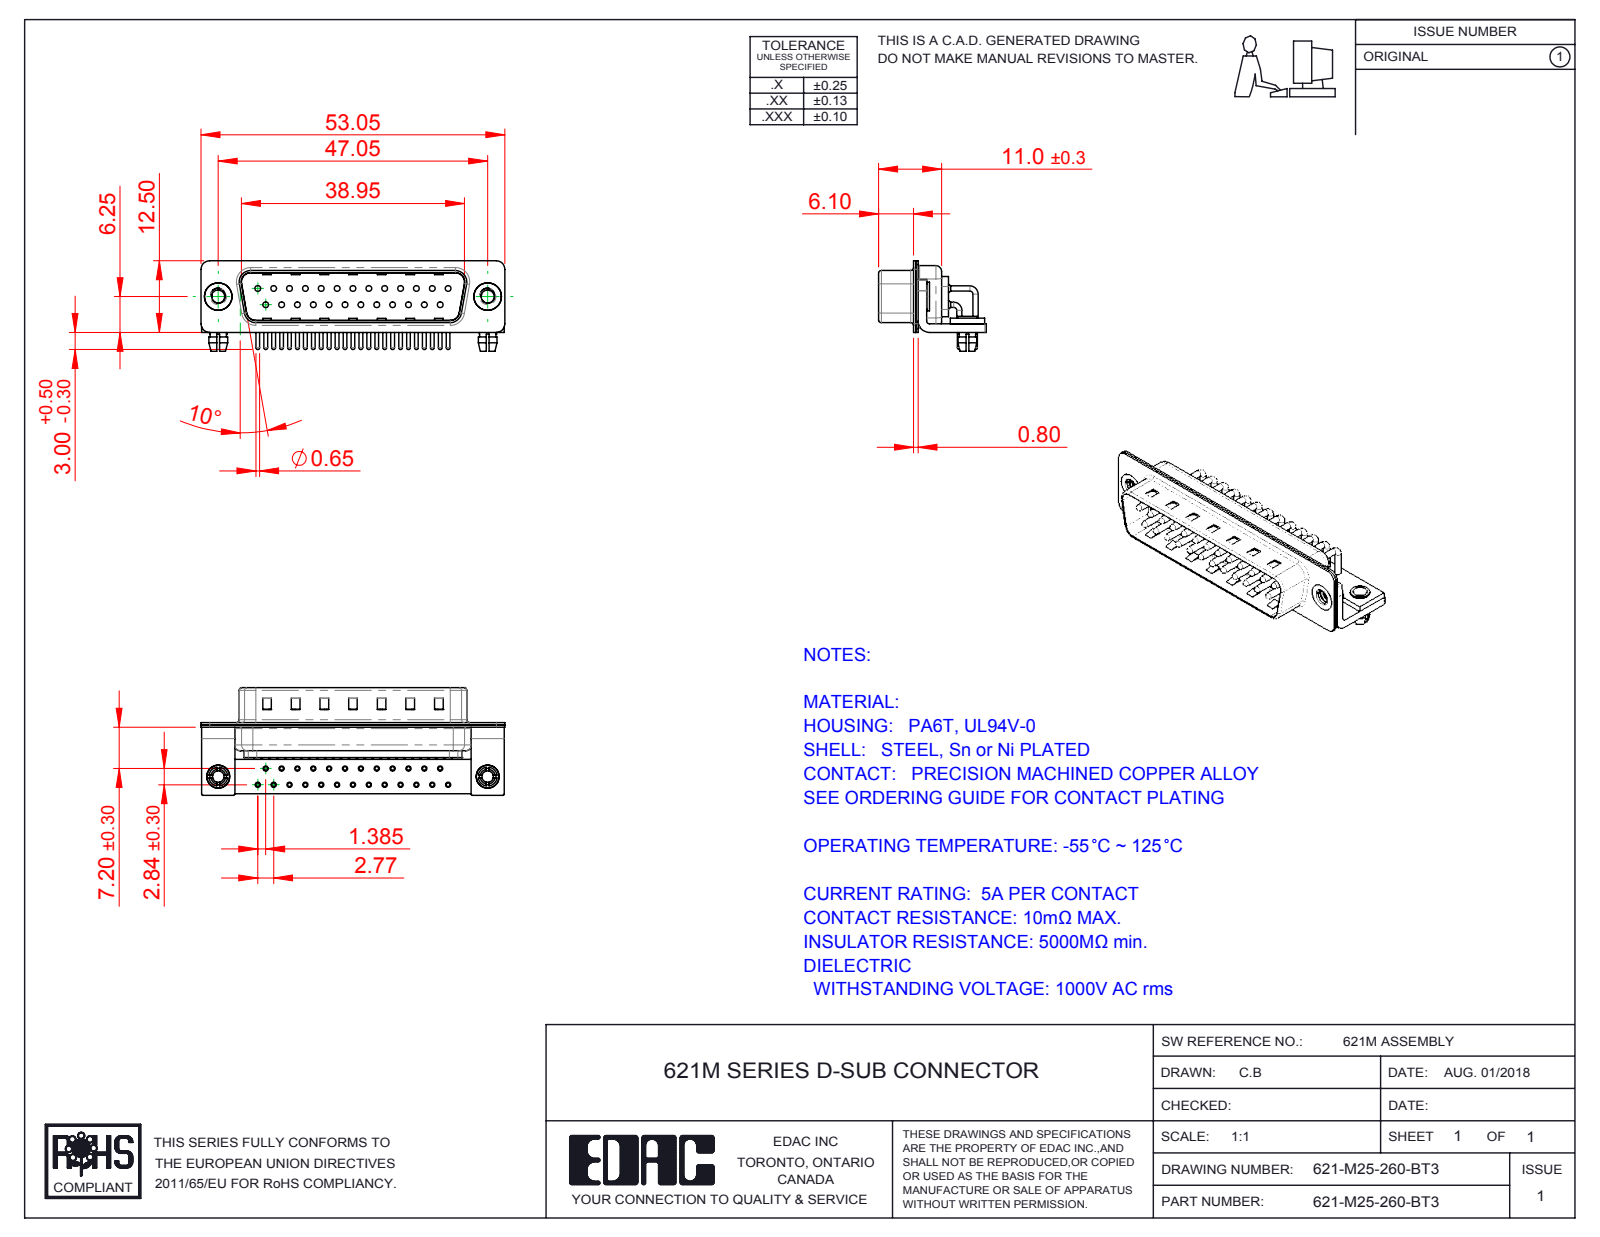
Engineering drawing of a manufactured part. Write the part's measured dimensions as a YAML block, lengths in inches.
part_name: "621M Contact Row 2; 621M Stabilizer Bracket; 621M 4-40 Threaded Rivet_Stabilizer; 621M Board Lock (+6 more)"
step_written_by: "SolidWorks 2016 (CONFIG_CONTROL_DESIGN)"
units: inches
bodies: {solids: 35, faces: 3318, planar: 1845, cylindrical: 1141, other: 332}
overall_size: [2.089, 0.74, 0.622]
volume: 0.209
surface_area: 14.15
round_holes:
  - {diameter: 0.079, count: 27}
  - {diameter: 0.035, count: 25}
  - {diameter: 0.039, count: 25}
  - {diameter: 0.067, count: 25}
  - {diameter: 0.089, count: 2}
  - {diameter: 0.098, count: 2}
  - {diameter: 0.126, count: 2}
  - {diameter: 0.157, count: 2}
  - {diameter: 0.189, count: 2}
round_bosses_or_shafts:
  - {diameter: 0.035, count: 33}
  - {diameter: 0.059, count: 25}
  - {diameter: 0.026, count: 25}
  - {diameter: 0.197, count: 2}
  - {diameter: 0.193, count: 2}
  - {diameter: 0.157, count: 2}
  - {diameter: 0.134, count: 2}
  - {diameter: 0.13, count: 2}
partial_cylinders:
  - {radius: 0.04, count: 25}
  - {radius: 0.01, count: 16}
  - {radius: 0.059, count: 16}
  - {radius: 0.079, count: 13}
  - {radius: 0.02, count: 9}
  - {radius: 0.063, count: 8}
  - {radius: 0.024, count: 4}
  - {radius: 0.026, count: 4}
face_to_face_distances: [0.016, 0.033, 0.049, 0.059, 0.376, 0.409, 0.031, 0.039, 0.327, 0.343]
hole_center_spacings: [0.124, 0.109, 0.327, 0.218, 0.436, 0.545, 0.198, 0.654]
